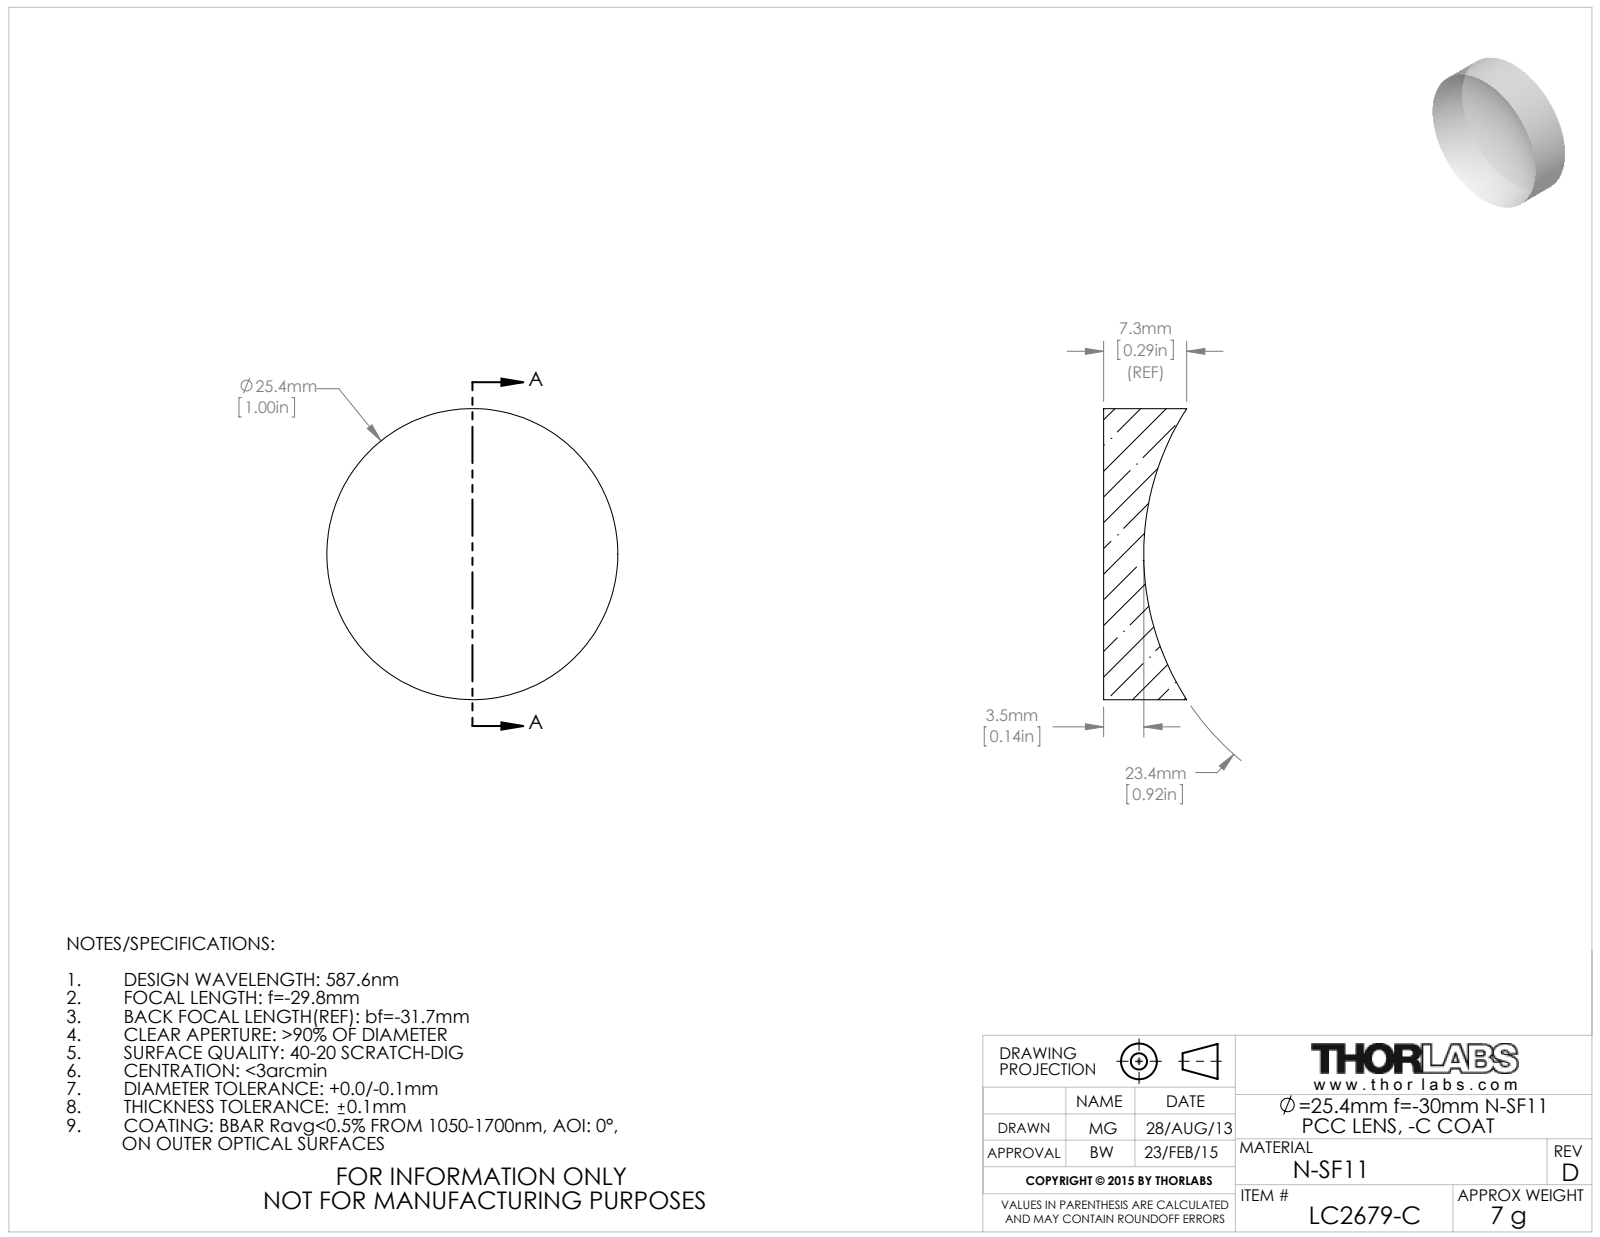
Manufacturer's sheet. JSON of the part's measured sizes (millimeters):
{"part_name": "5444-E0W", "step_written_by": "SolidWorks 2014 (CONFIG_CONTROL_DESIGN)", "units": "millimeters", "bodies": {"solids": 1, "faces": 5, "planar": 1, "cylindrical": 2, "other": 2}, "overall_size": [25.4, 25.4, 7.26], "volume_mm3": 2697, "surface_area_mm2": 1637, "round_bosses_or_shafts": [[25.4, 1]]}
